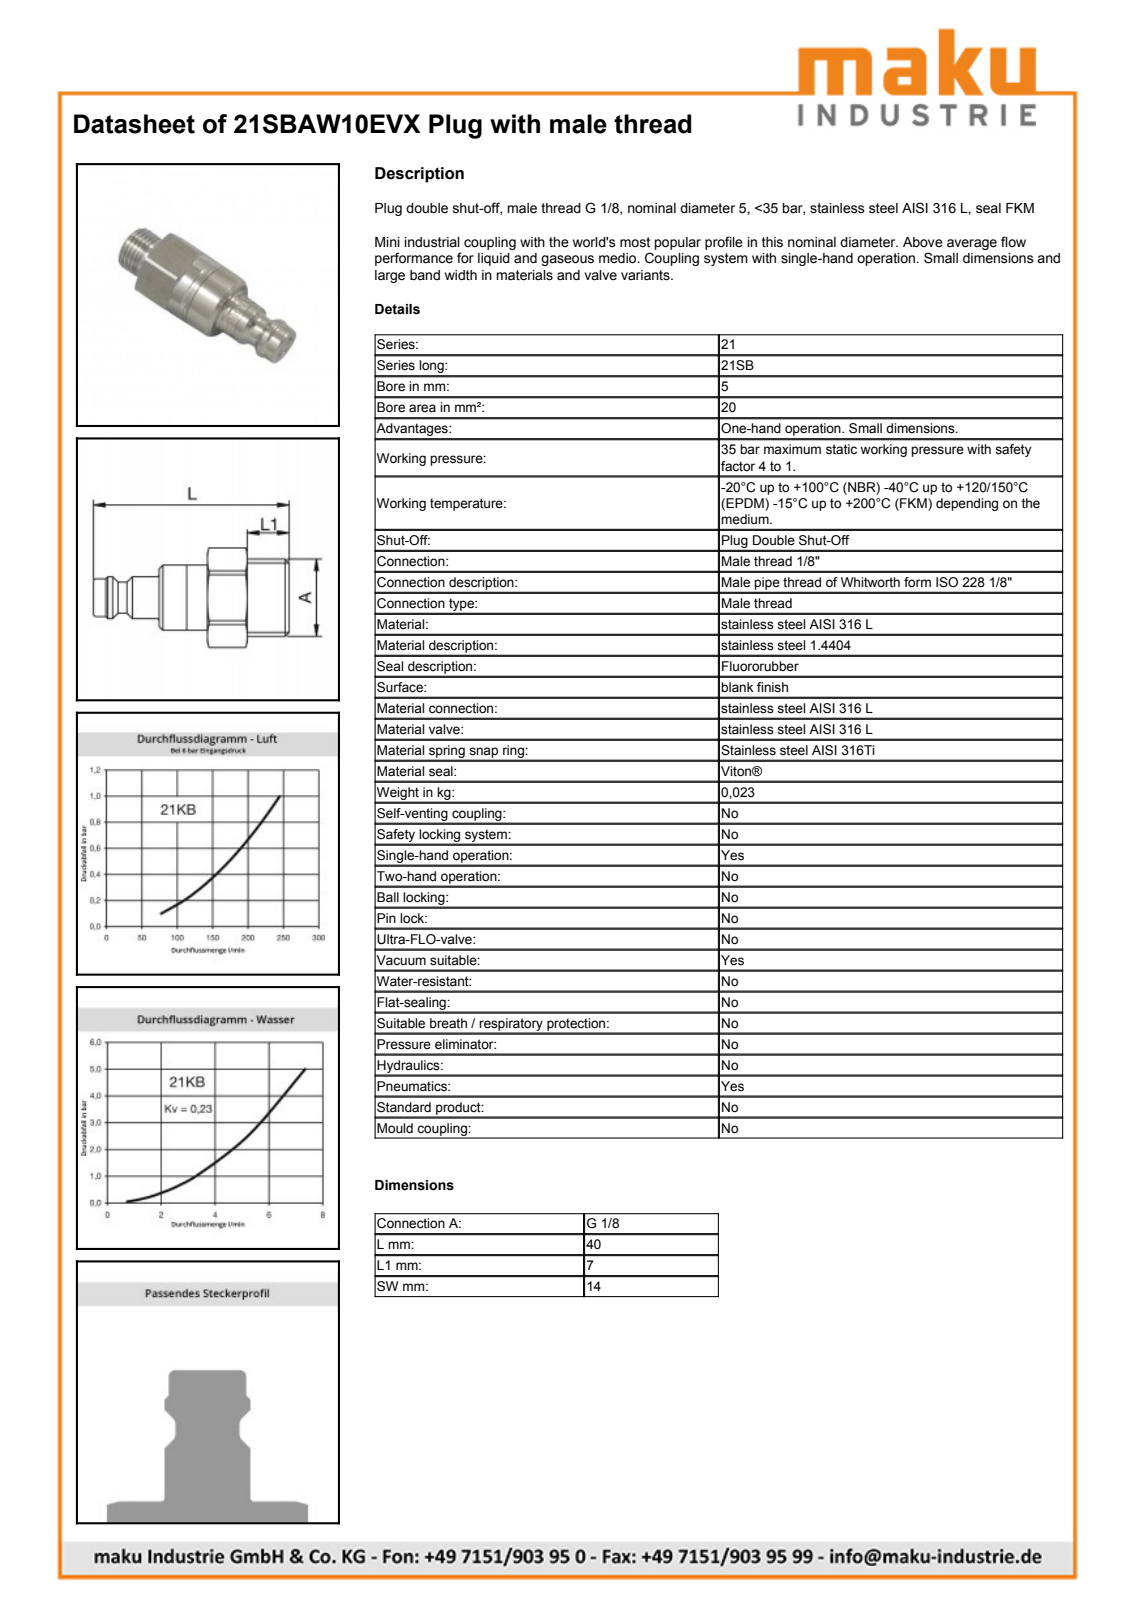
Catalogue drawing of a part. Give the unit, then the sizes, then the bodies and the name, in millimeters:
Units: millimetres
Overall size (bounding box): 40 × 15.8 × 14.19
Round holes (diameter × count): ⌀12 ×1
Round bosses / shafts (diameter × count): ⌀14 ×1, ⌀10.94 ×1, ⌀9.73 ×1, ⌀9 ×1, ⌀8.1 ×1, ⌀6.7 ×1
Partial cylindrical surfaces — rounded edges, fillets, slot ends (radius × count): R7.9 ×1
Main face-to-face distances: 14, 7, 18.9, 25.9, 14.1, 33, 40, 20, 25, 10.9
Volume: 4 234 mm³ · Surface area: 2 039 mm²
Bodies: 1 solid, 56 faces (13 planar, 16 cylindrical, 27 other)
Part name (STEP PRODUCT): D105249
STEP written by: Autodesk Inventor 2011 (AUTOMOTIVE_DESIGN)
